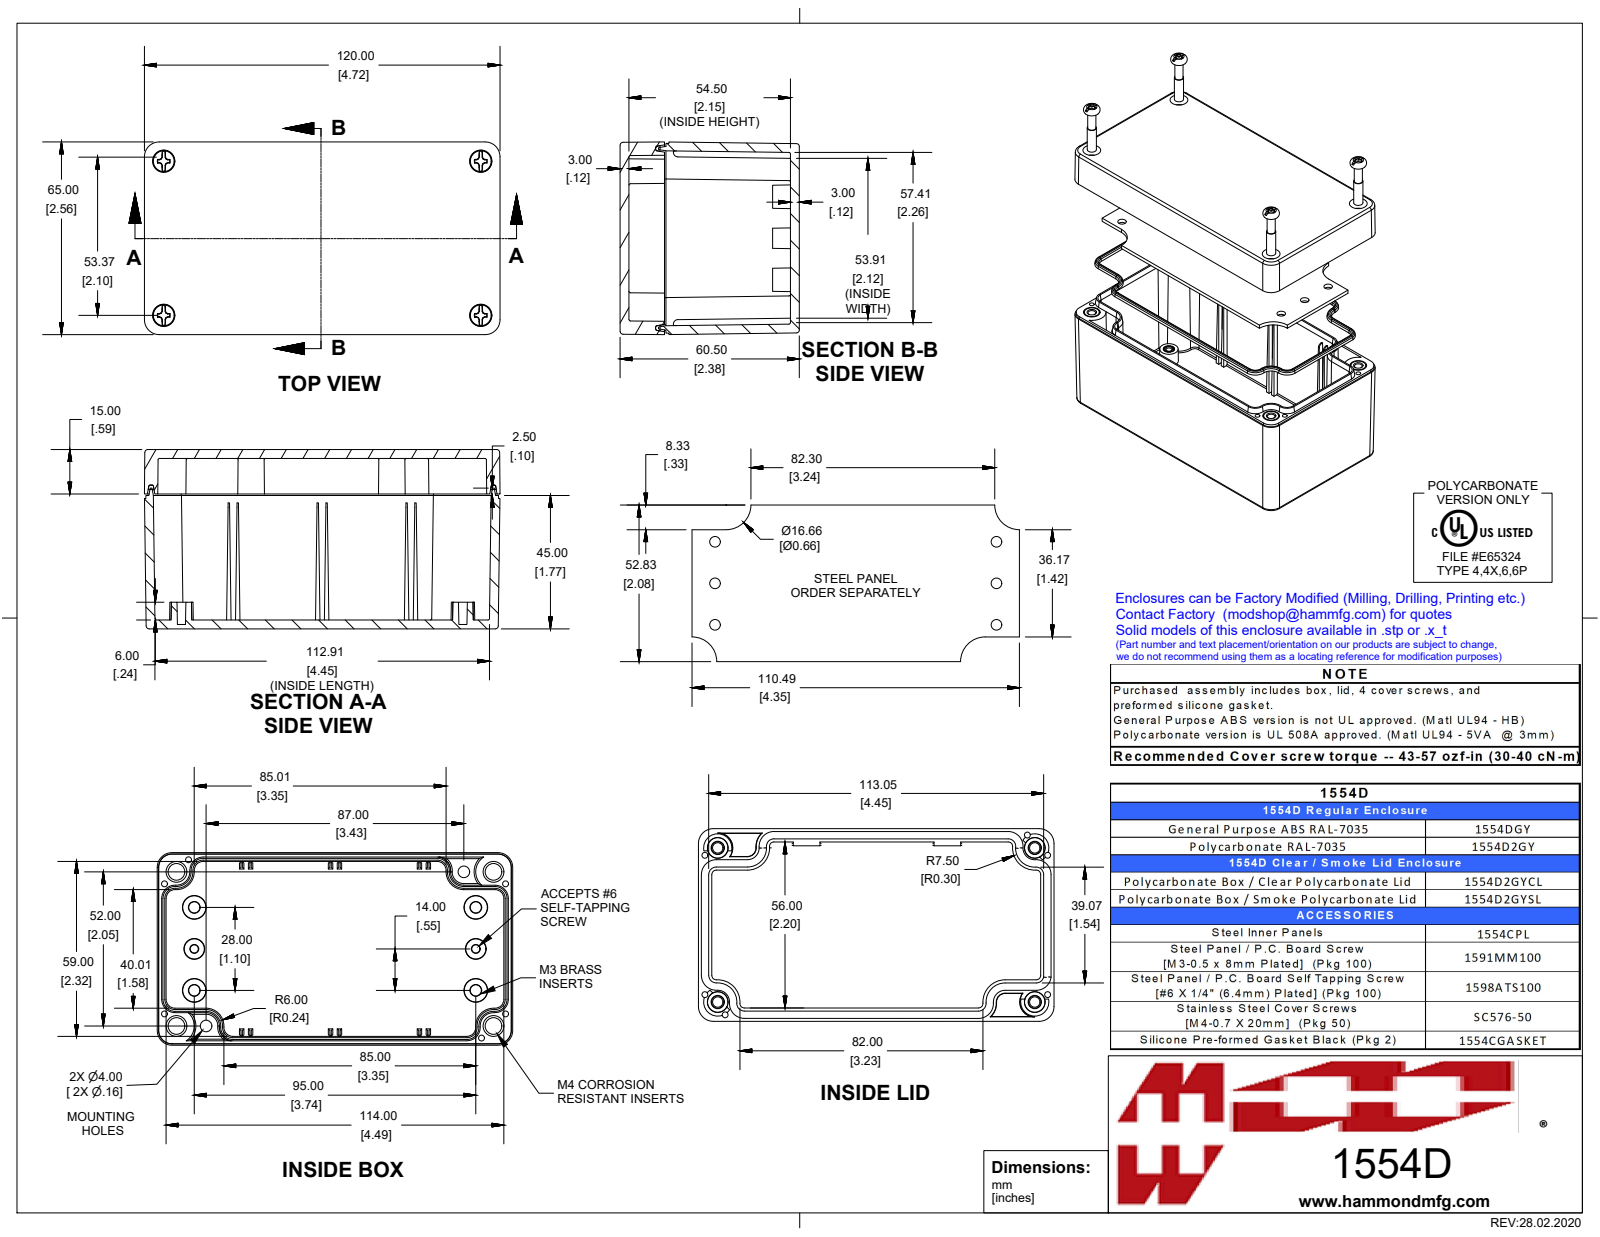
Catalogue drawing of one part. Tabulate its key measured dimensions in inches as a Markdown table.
| quantity | value |
| --- | --- |
| part name | 1554D2GY |
| STEP written by | SolidWorks 2019 (AUTOMOTIVE_DESIGN) |
| units | inches |
| bodies | 15 solids, 1306 faces (354 planar, 338 cylindrical, 614 other) |
| overall size | 4.724 × 2.559 × 2.382 |
| volume | 7.477 in³ |
| surface area | 140.1 in² |
| round holes (diameter × count) | 0.079 × 12, 0.097 × 4, 0.128 × 4, 0.138 × 4, 0.276 × 4 |
| round bosses / shafts (diameter × count) | 0.25 × 4, 0.218 × 4, 0.21 × 4, 0.19 × 4, 0.154 × 4, 0.153 × 4, 0.15 × 4, 0.135 × 4 |
| partial cylindrical surfaces (radius × count) | 0.02 × 39, 0.039 × 8, 0.197 × 8, 0.187 × 4, 0.059 × 2 |
| main face-to-face distances | 0.118, 2.264, 2.382, 2.146, 0.059, 0.177, 0.492, 0.079, 1.791, 0.472 |
| hole center spacings | 0.197, 0.226, 0.42, 1.956, 4.384, 4.684, 4.797, 0.062 |
